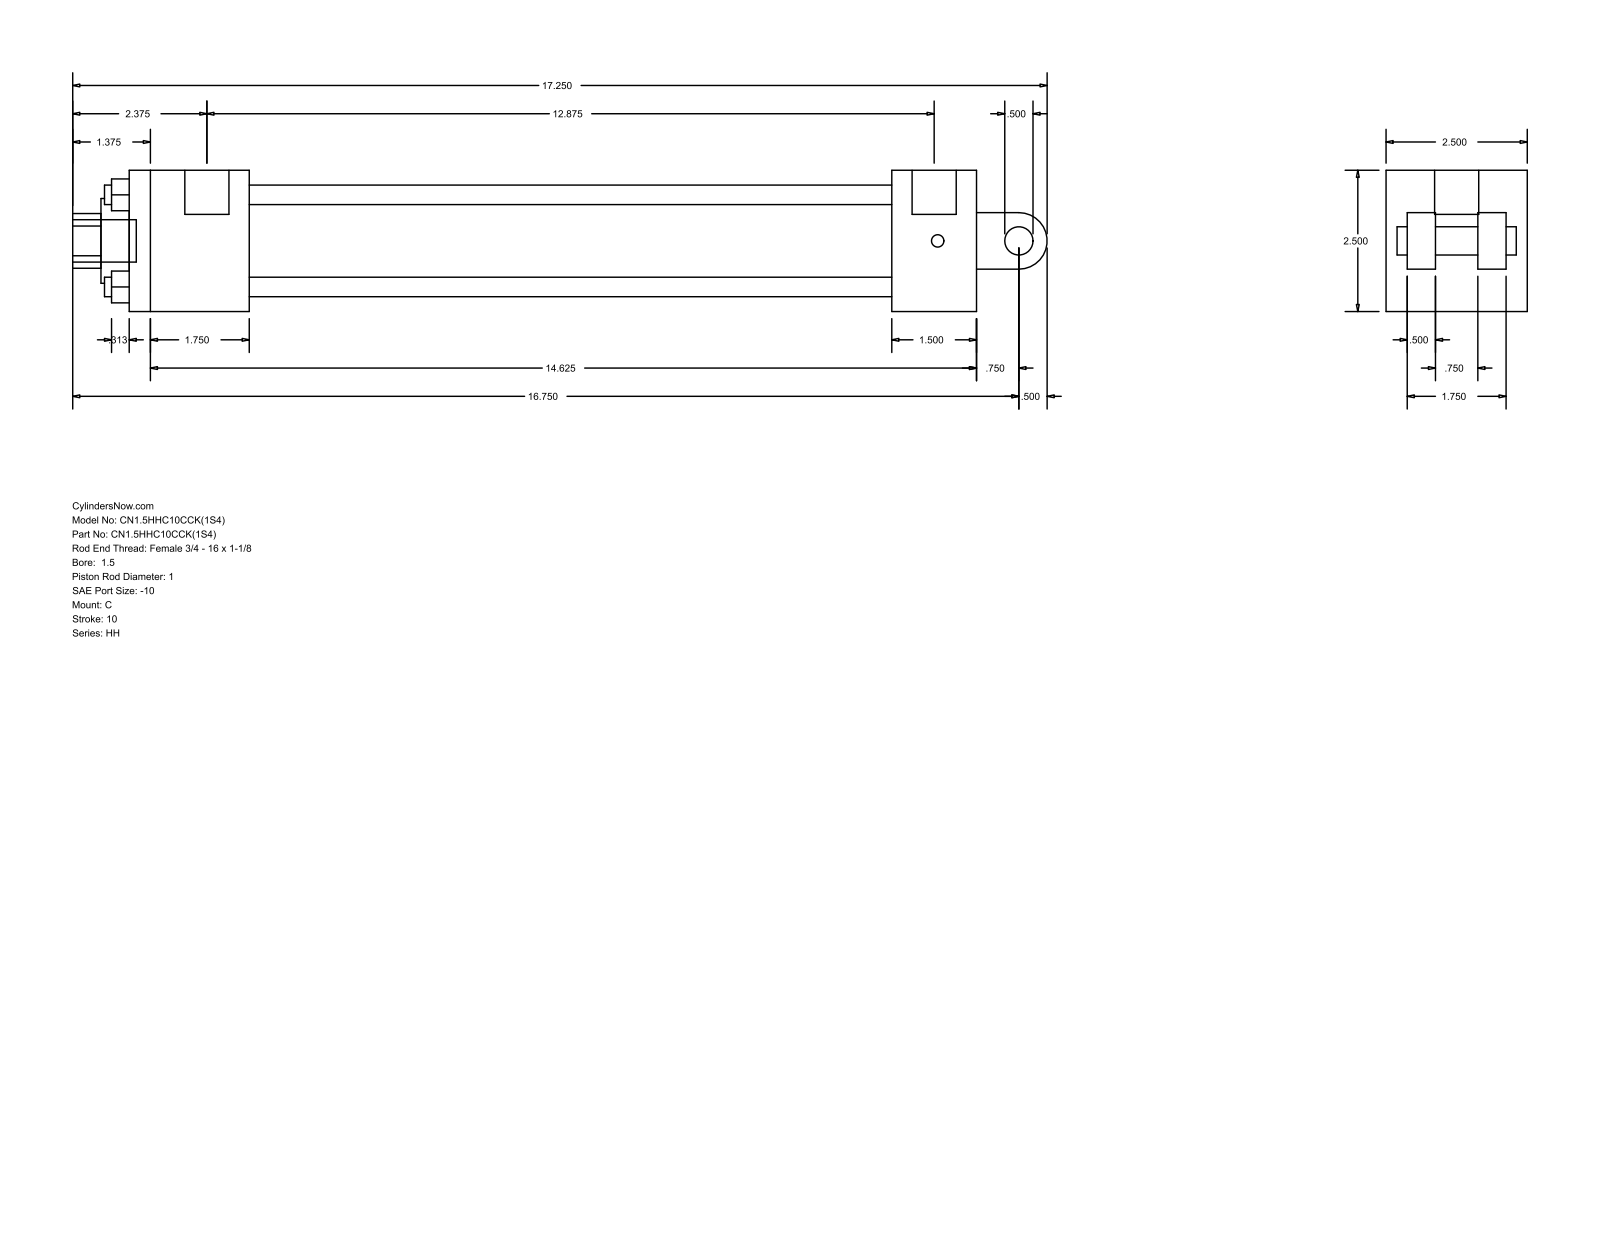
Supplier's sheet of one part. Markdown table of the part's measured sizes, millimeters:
| quantity | value |
| --- | --- |
| part name | HH_C__0150_1 |
| STEP written by | GSSL Pune (CONFIG_CONTROL_DESIGN) |
| units | millimeters |
| bodies | 0 solids, 99 faces (70 planar, 29 cylindrical, 0 other) |
| overall size | 438.15 × 63.5 × 63.5 |
| round holes (diameter × count) | 8.76 × 4, 5.56 × 2, 19.84 × 1, 25.4 × 1, 38.1 × 1, 44.45 × 1 |
| round bosses / shafts (diameter × count) | 5.56 × 2, 19.84 × 1, 19.05 × 1, 12.7 × 1 |
| partial cylindrical surfaces (radius × count) | 12.29 × 1, 12.7 × 1 |
| main face-to-face distances | 63.5, 53.98, 288.92, 327.02, 38.1, 342.9, 381, 12.7, 22.22, 41.28 |
| hole center spacings | 29.27, 41.4, 58.55, 1.59 |
